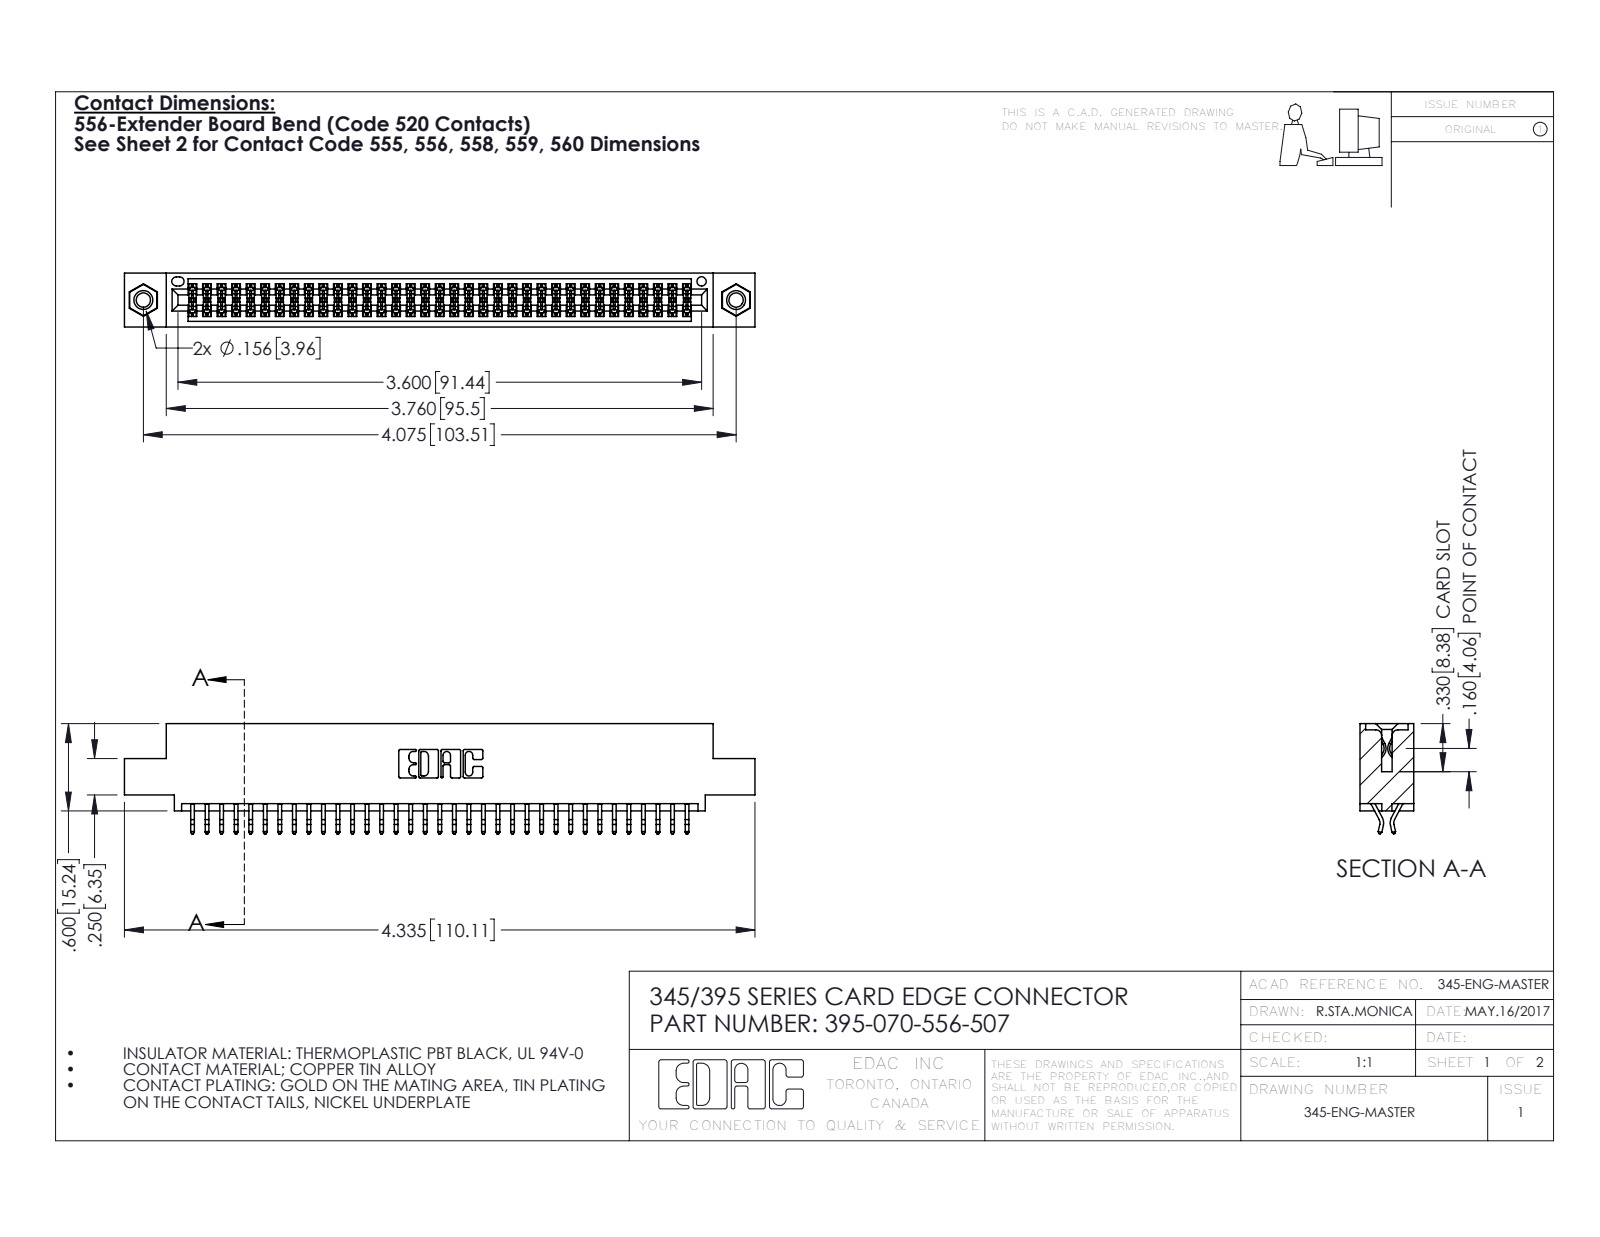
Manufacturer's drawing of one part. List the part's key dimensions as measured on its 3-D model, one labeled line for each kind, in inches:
Part name (STEP PRODUCT): 395-070-556-507; 345 Part_0.110 Offset - 0.156 Dia-TI; 345-250-001_345-250-005-103; 345-292-001_556 Tail
STEP written by: SolidWorks 2016 (CONFIG_CONTROL_DESIGN)
Units: inches
Bodies: 73 solids, 4110 faces (2706 planar, 1388 cylindrical, 16 other)
Overall size (bounding box): 4.335 × 0.757 × 0.37
Volume: 0.643 in³ · Surface area: 24.03 in²
Round holes (diameter × count): ⌀0.098 ×2, ⌀0.125 ×2, ⌀0.156 ×2, ⌀0.064 ×1
Round bosses / shafts (diameter × count): ⌀0.155 ×2
Partial cylindrical surfaces — rounded edges, fillets, slot ends (radius × count): R0.006 ×105, R0.01 ×22, R0.007 ×6, R0.031 ×6, R0.026 ×3, R0.01 ×2, R0.014 ×2, R0.019 ×2
Main face-to-face distances: 0.072, 0.298, 0.37, 0.2, 0.025, 0.098, 0.272, 0.225, 0.175, 0.149
Hole centre spacings: 0.27, 3.839, 4.075
